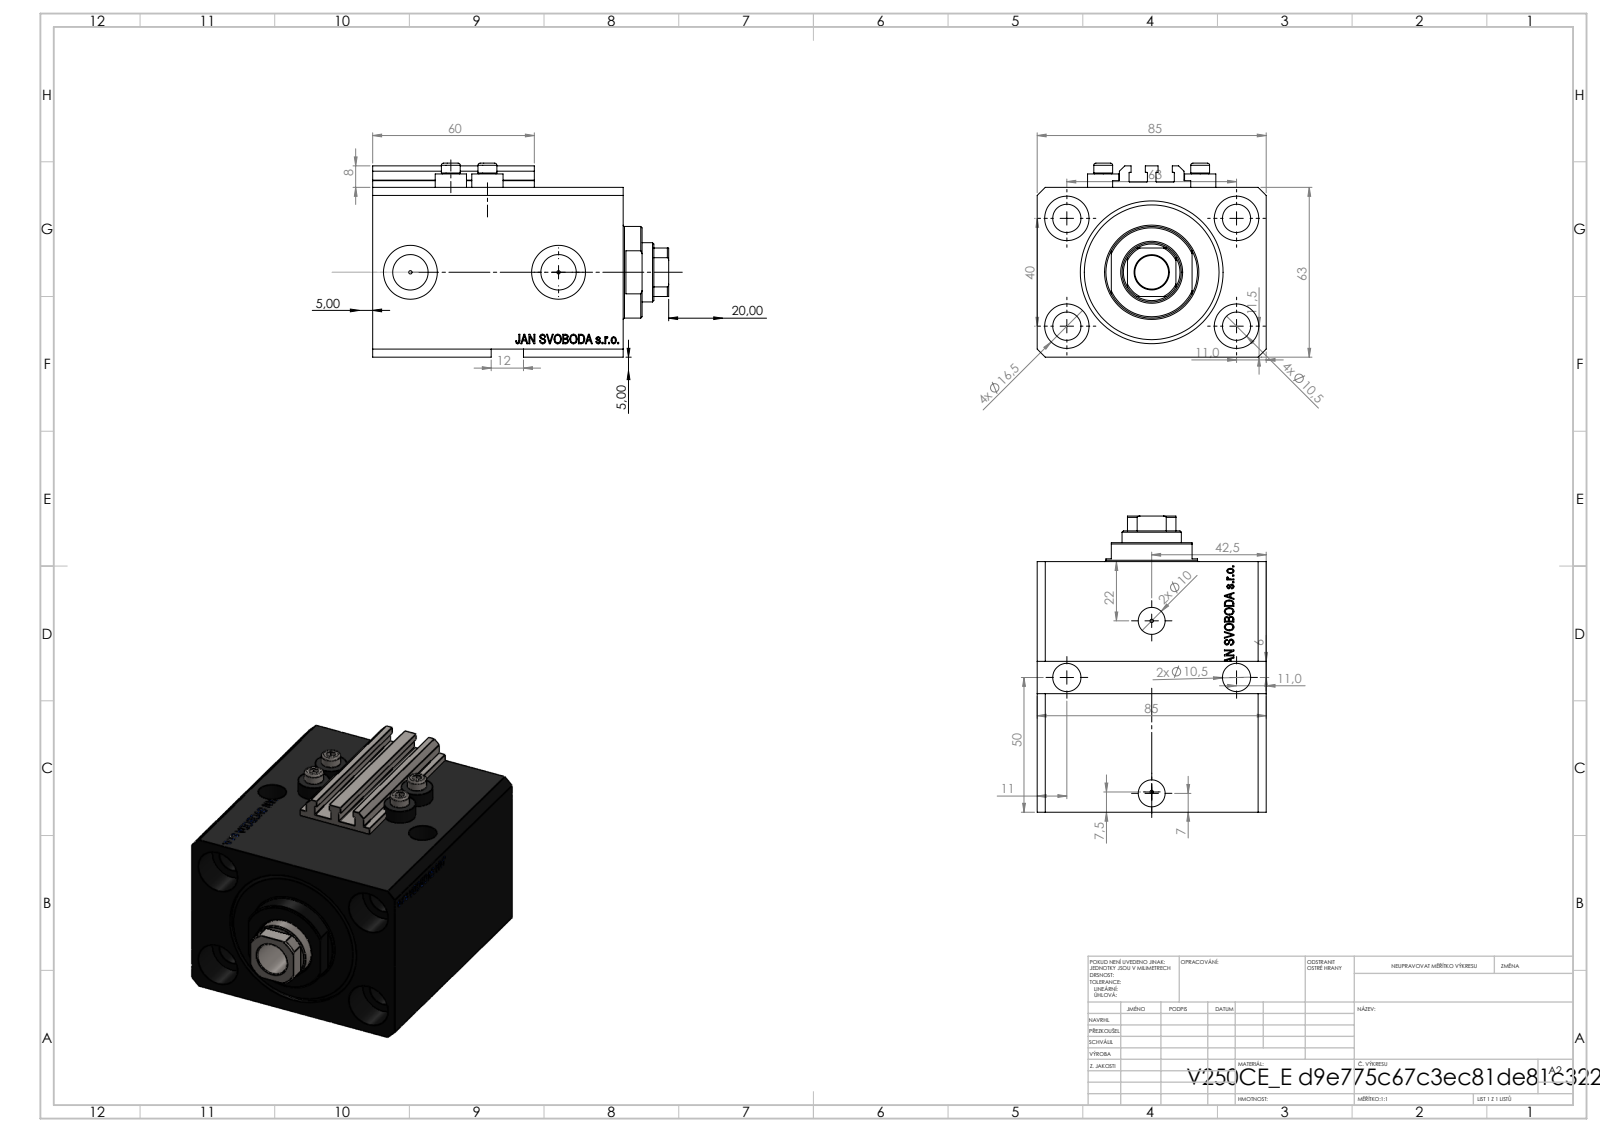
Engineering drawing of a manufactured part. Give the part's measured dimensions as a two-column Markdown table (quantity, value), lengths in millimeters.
| quantity | value |
| --- | --- |
| part name | V250CE_C_VCP; V250CE_E_Body; ALLEN BOLT V250CE; V250CE_VC_E |
| STEP written by | SolidWorks 2019 (CONFIG_CONTROL_DESIGN) |
| units | millimeters |
| bodies | 8 solids, 1087 faces (535 planar, 126 cylindrical, 426 other) |
| overall size | 110 × 85 × 72 |
| volume | 437 253 mm³ |
| surface area | 95 786 mm² |
| round holes (diameter × count) | 10.5 × 6, 1.25 × 4, 4 × 4, 16.5 × 4, 10 × 2, 13.16 × 2, 20 × 2, 12.5 × 1, 22 × 1, 40 × 1, 53 × 1 |
| round bosses / shafts (diameter × count) | 11.6 × 4, 7 × 4, 34 × 1 |
| partial cylindrical surfaces (radius × count) | 0.2 × 10, 10.5 × 1 |
| main face-to-face distances | 63, 85, 93, 17, 76, 11.4, 64.6, 81.6, 3, 65 |
| hole center spacings | 37.31, 63, 13.6, 15.4, 24.96, 28.02, 28.43, 33.62 |
